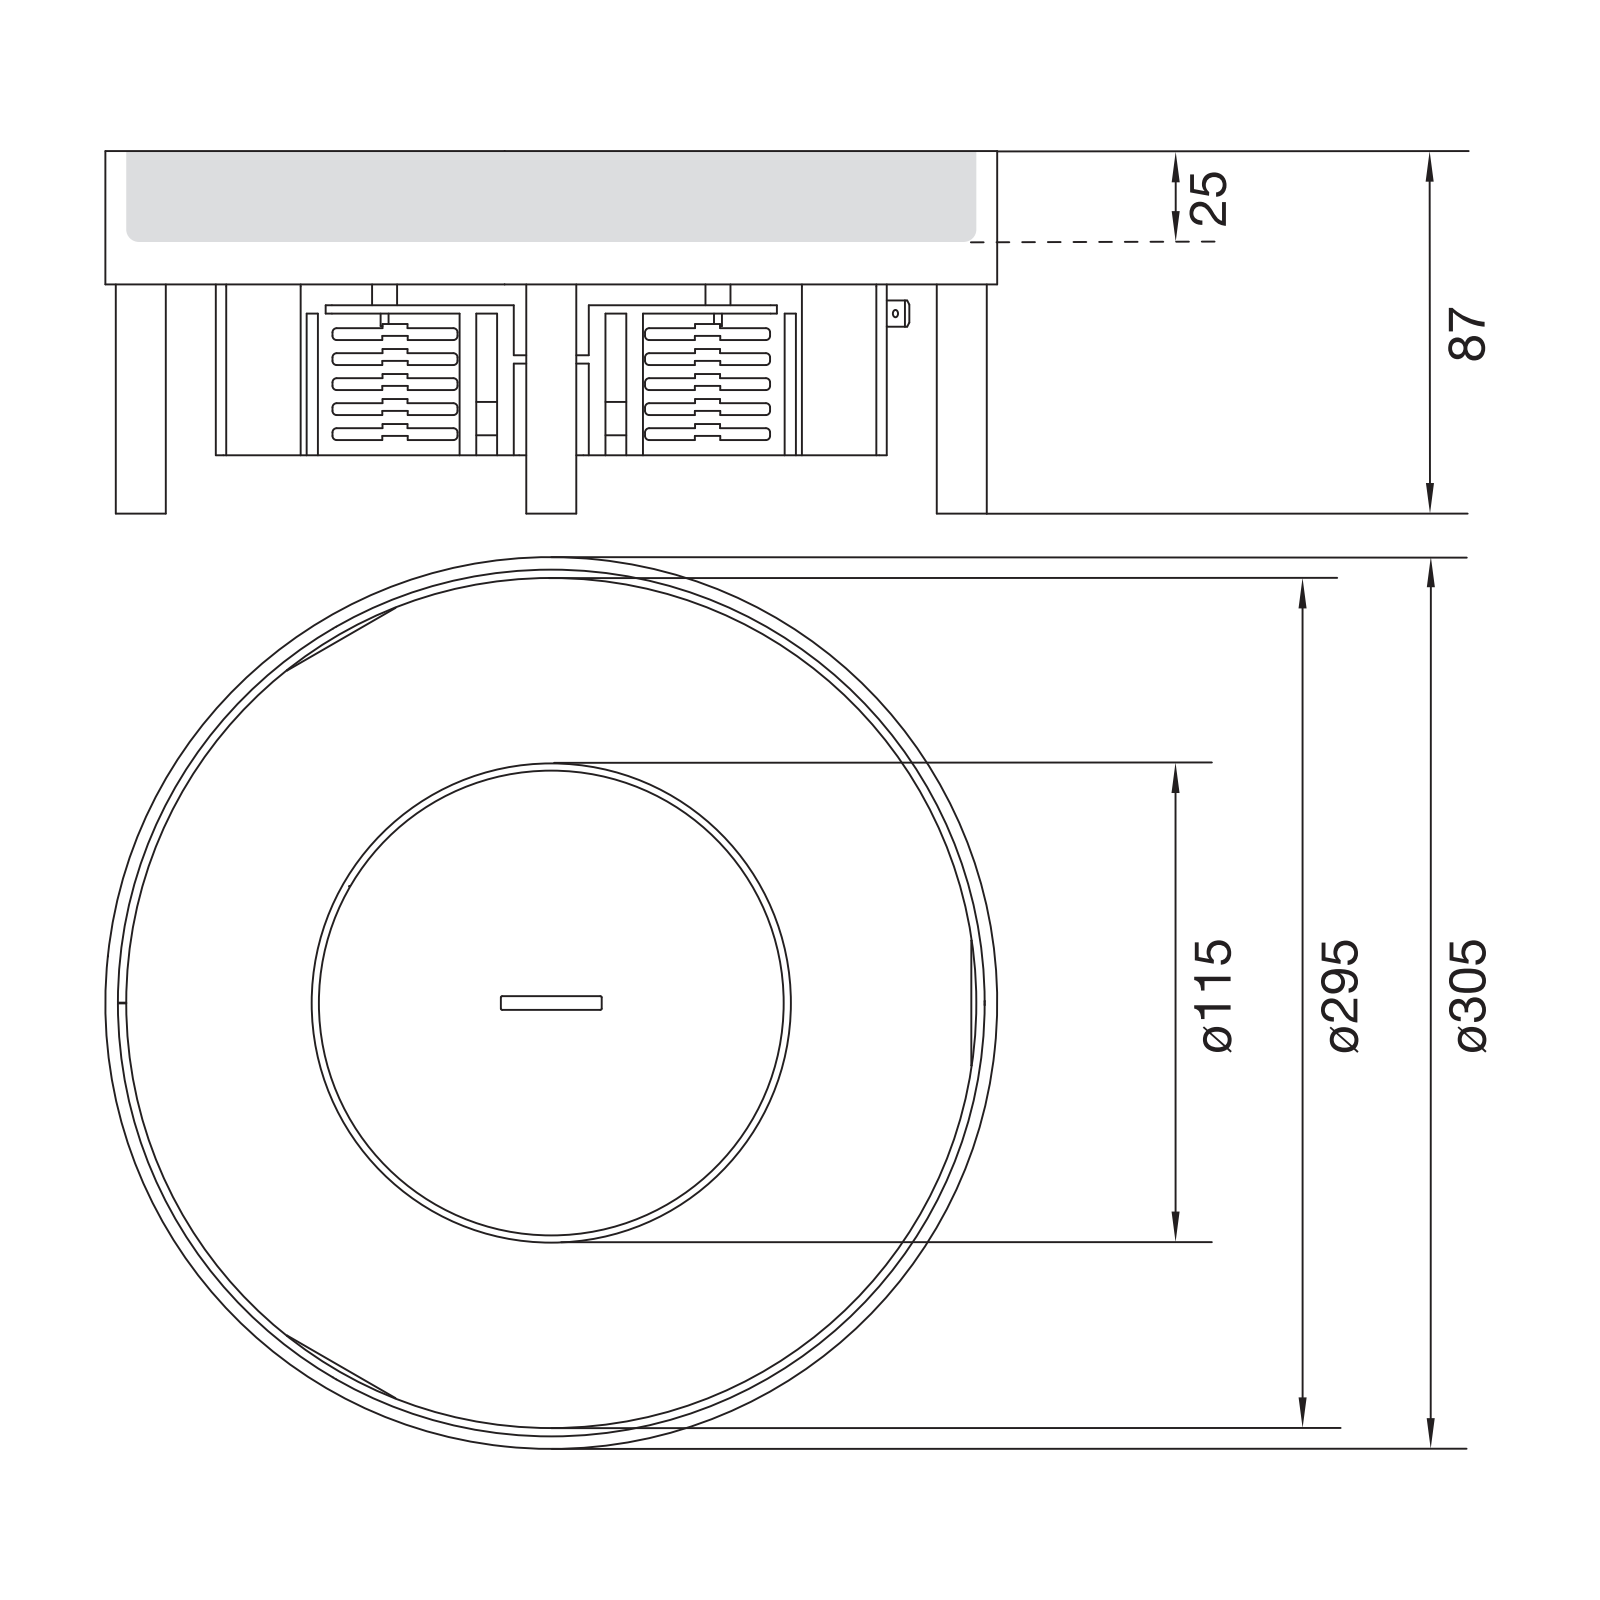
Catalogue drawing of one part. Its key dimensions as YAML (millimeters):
part_name: "T-00702; T-00703; T-00704; T-00709 (+8 more)"
step_written_by: "CREO PARAMETRIC BY PTC INC, 2022024 (AUTOMOTIVE_DESIGN)"
units: millimeters
bodies: {solids: 16, faces: 225, planar: 98, cylindrical: 117, other: 10}
overall_size: [305, 305, 87]
volume: 459240
surface_area: 447353
round_holes:
  - {diameter: 3.8, count: 6}
  - {diameter: 6.8, count: 4}
  - {diameter: 8.5, count: 4}
  - {diameter: 10.1, count: 4}
  - {diameter: 4.5, count: 3}
  - {diameter: 80.59, count: 1}
  - {diameter: 90, count: 1}
  - {diameter: 101, count: 1}
  - {diameter: 107, count: 1}
  - {diameter: 108.6, count: 1}
  - {diameter: 111.4, count: 1}
  - {diameter: 112, count: 1}
round_bosses_or_shafts:
  - {diameter: 12, count: 4}
  - {diameter: 9.85, count: 4}
  - {diameter: 305, count: 1}
  - {diameter: 301, count: 1}
  - {diameter: 299, count: 1}
  - {diameter: 295, count: 1}
  - {diameter: 115, count: 1}
  - {diameter: 111.6, count: 1}
partial_cylinders:
  - {radius: 0.5, count: 8}
  - {radius: 5, count: 3}
  - {radius: 43, count: 1}
  - {radius: 150, count: 1}
face_to_face_distances: [2, 5, 2.5, 7, 3, 25, 228.5, 229.5, 30, 27]
hole_center_spacings: [59.51, 127.05, 140, 143.6, 197.99, 225.52, 260.65, 54]
